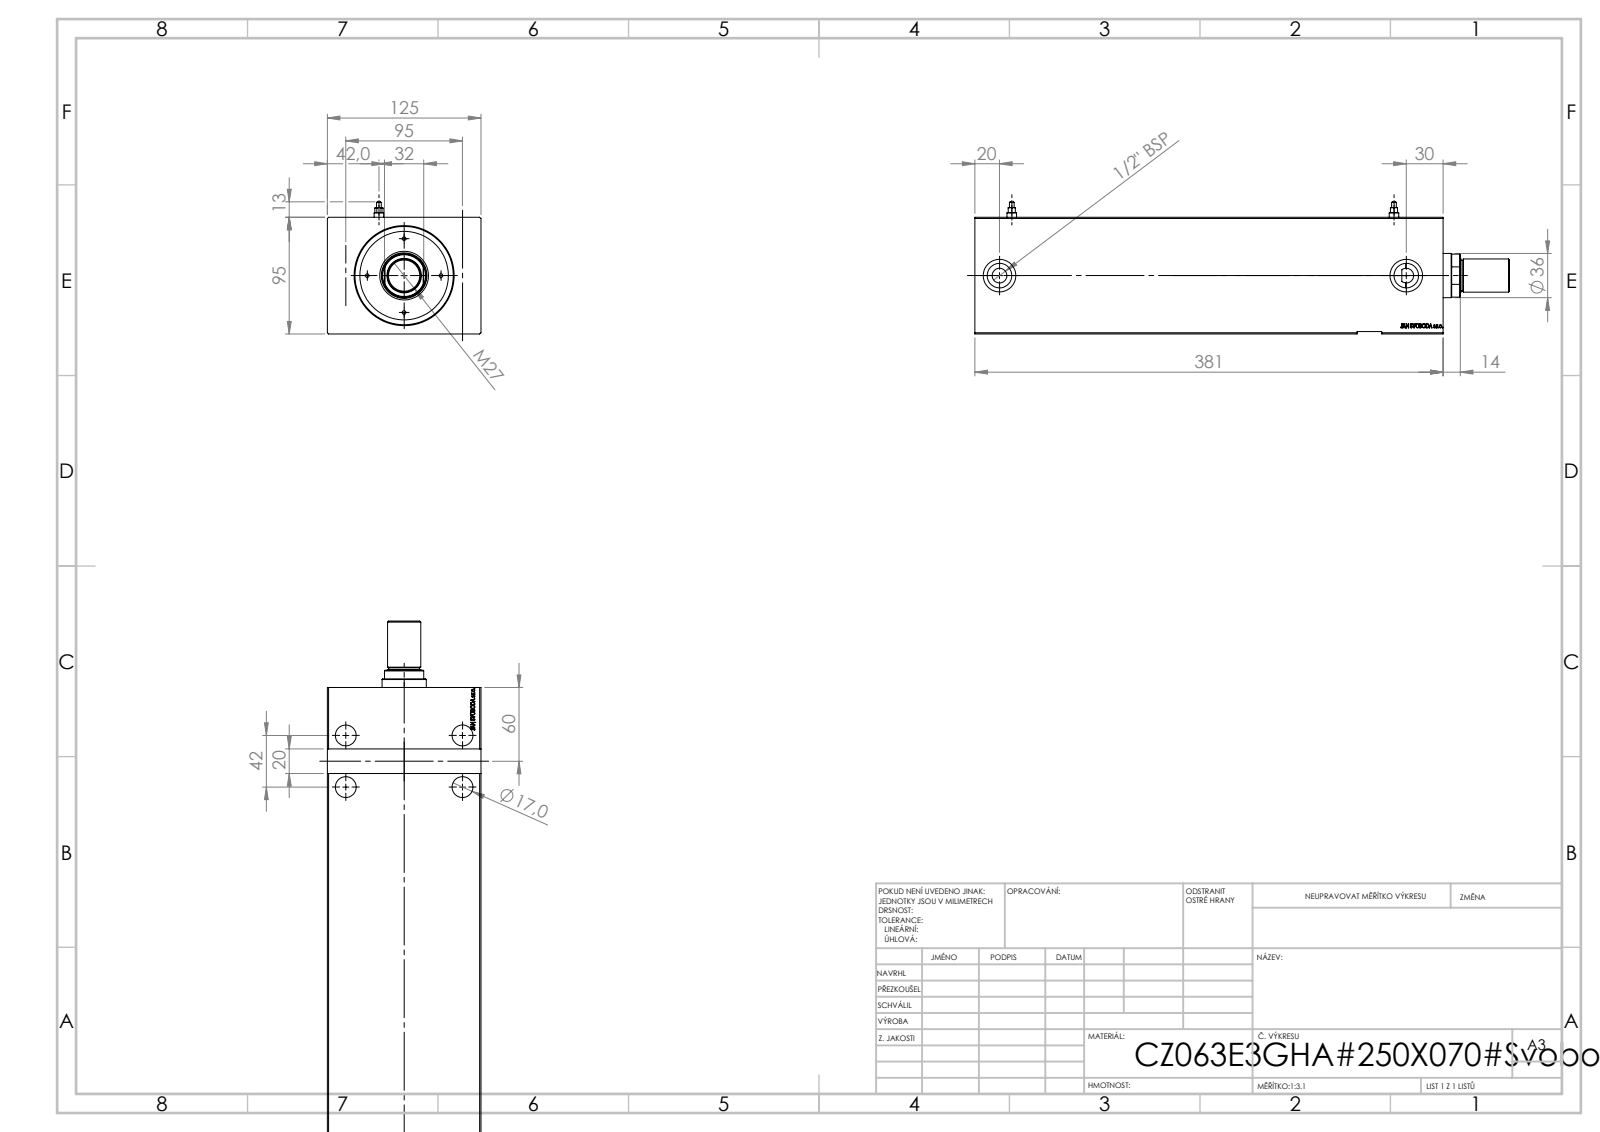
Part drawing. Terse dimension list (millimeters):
written by: SolidWorks 2019 (CONFIG_CONTROL_DESIGN)
unit: mm
bodies: 1 solid, 805 faces (393 planar, 30 cylindrical, 382 other)
size: 381 × 125 × 95
volume: 3 273 000 mm³; area: 283 111 mm²
holes: 4× ⌀17, 2× ⌀8, 2× ⌀20, 2× ⌀26.5, 1× ⌀12, 1× ⌀36, 1× ⌀63, 1× ⌀80
rounds: 1× R6
face distances: 95, 125, 381, 360.2, 20.8, 2, 93, 14, 346.2, 367
hole spacings: 42, 95, 103.87, 27.02, 49.09, 68.01, 79.4, 271.35
